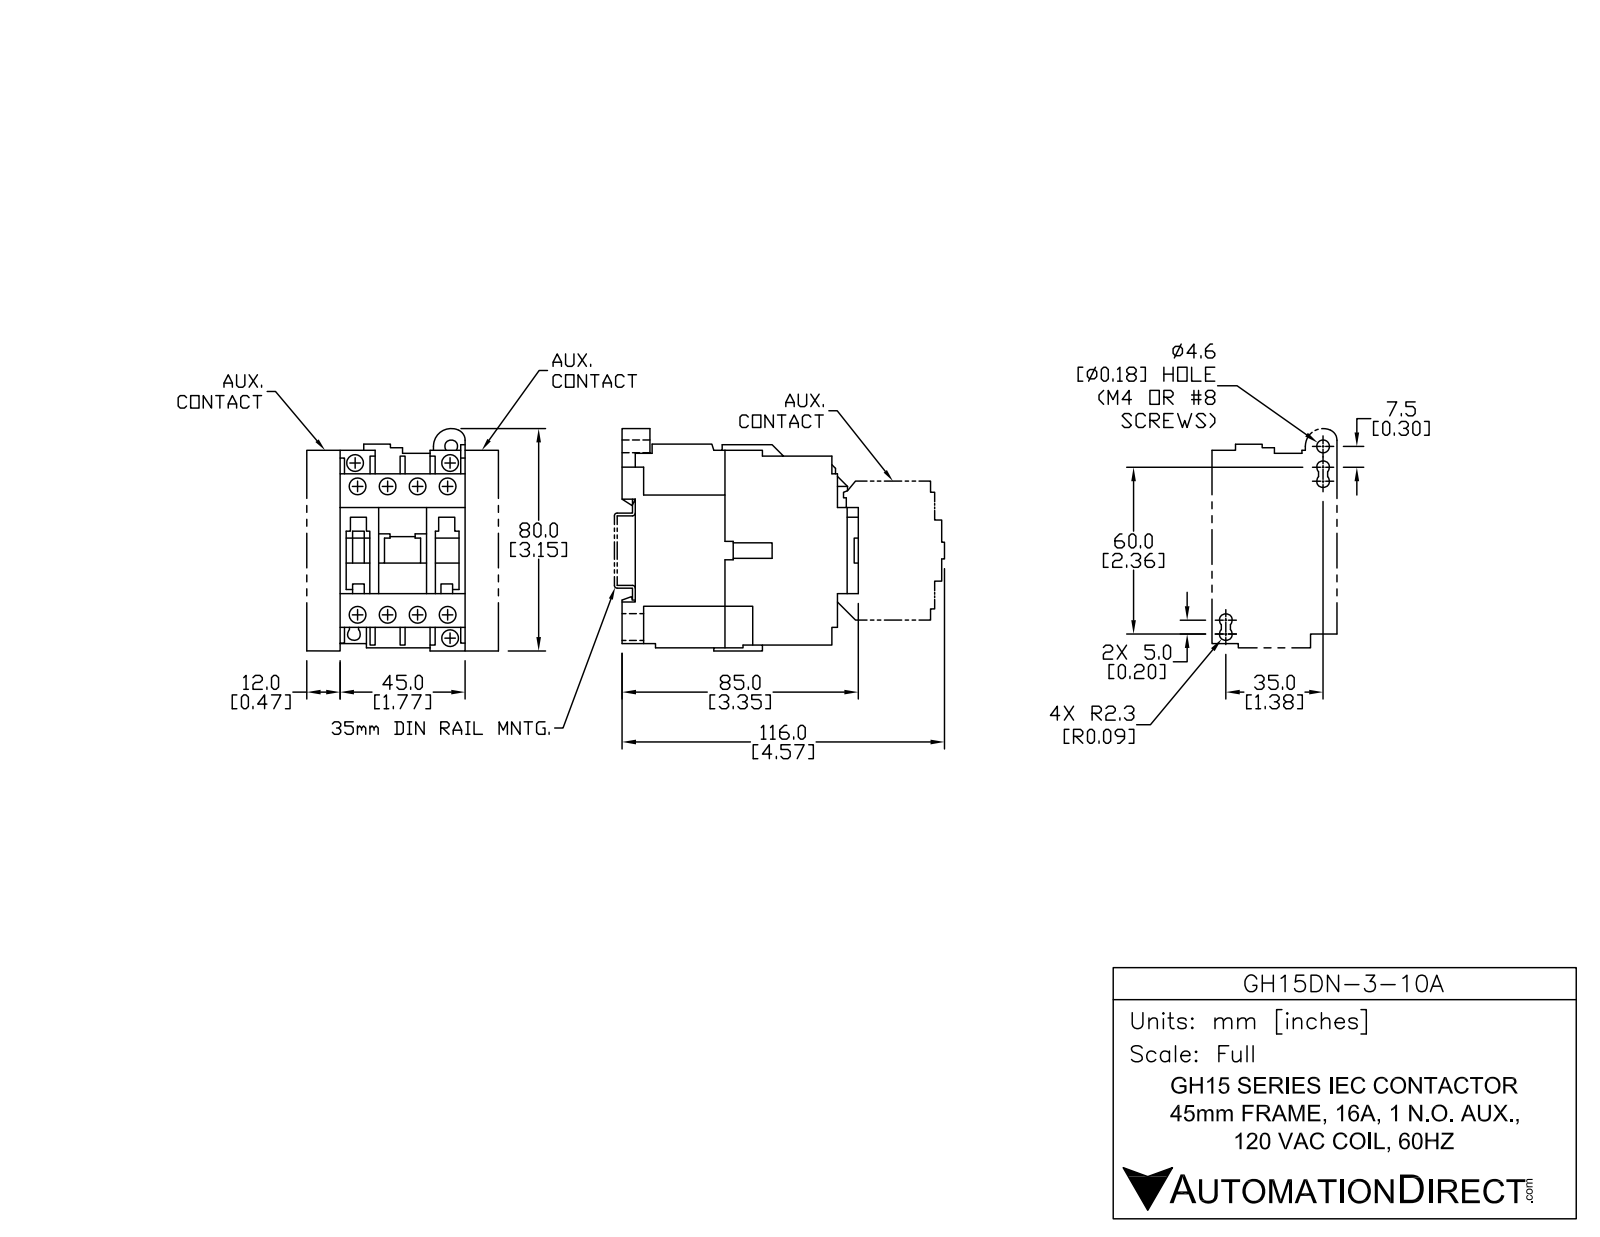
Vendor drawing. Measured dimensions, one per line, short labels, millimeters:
name: GH15DN-3-10A
written by: SolidWorks 2009 (AUTOMOTIVE_DESIGN)
unit: mm
bodies: 1 solid, 666 faces (447 planar, 65 cylindrical, 154 other)
size: 85.5 × 80 × 45
volume: 196 351 mm³; area: 35 792 mm²
holes: 9× ⌀6.25, 2× ⌀6.5, 1× ⌀4.6
rounds: 10× R1, 8× R2.3, 8× R4.75, 2× R3, 1× R4.99, 1× R5
face distances: 45, 9.5, 35.5, 12.12, 23.38, 8, 7, 33.75, 10.38, 32.87
hole spacings: 11.25, 47.12, 22.5, 45.76, 50.99, 7.62, 33.75, 53.38
